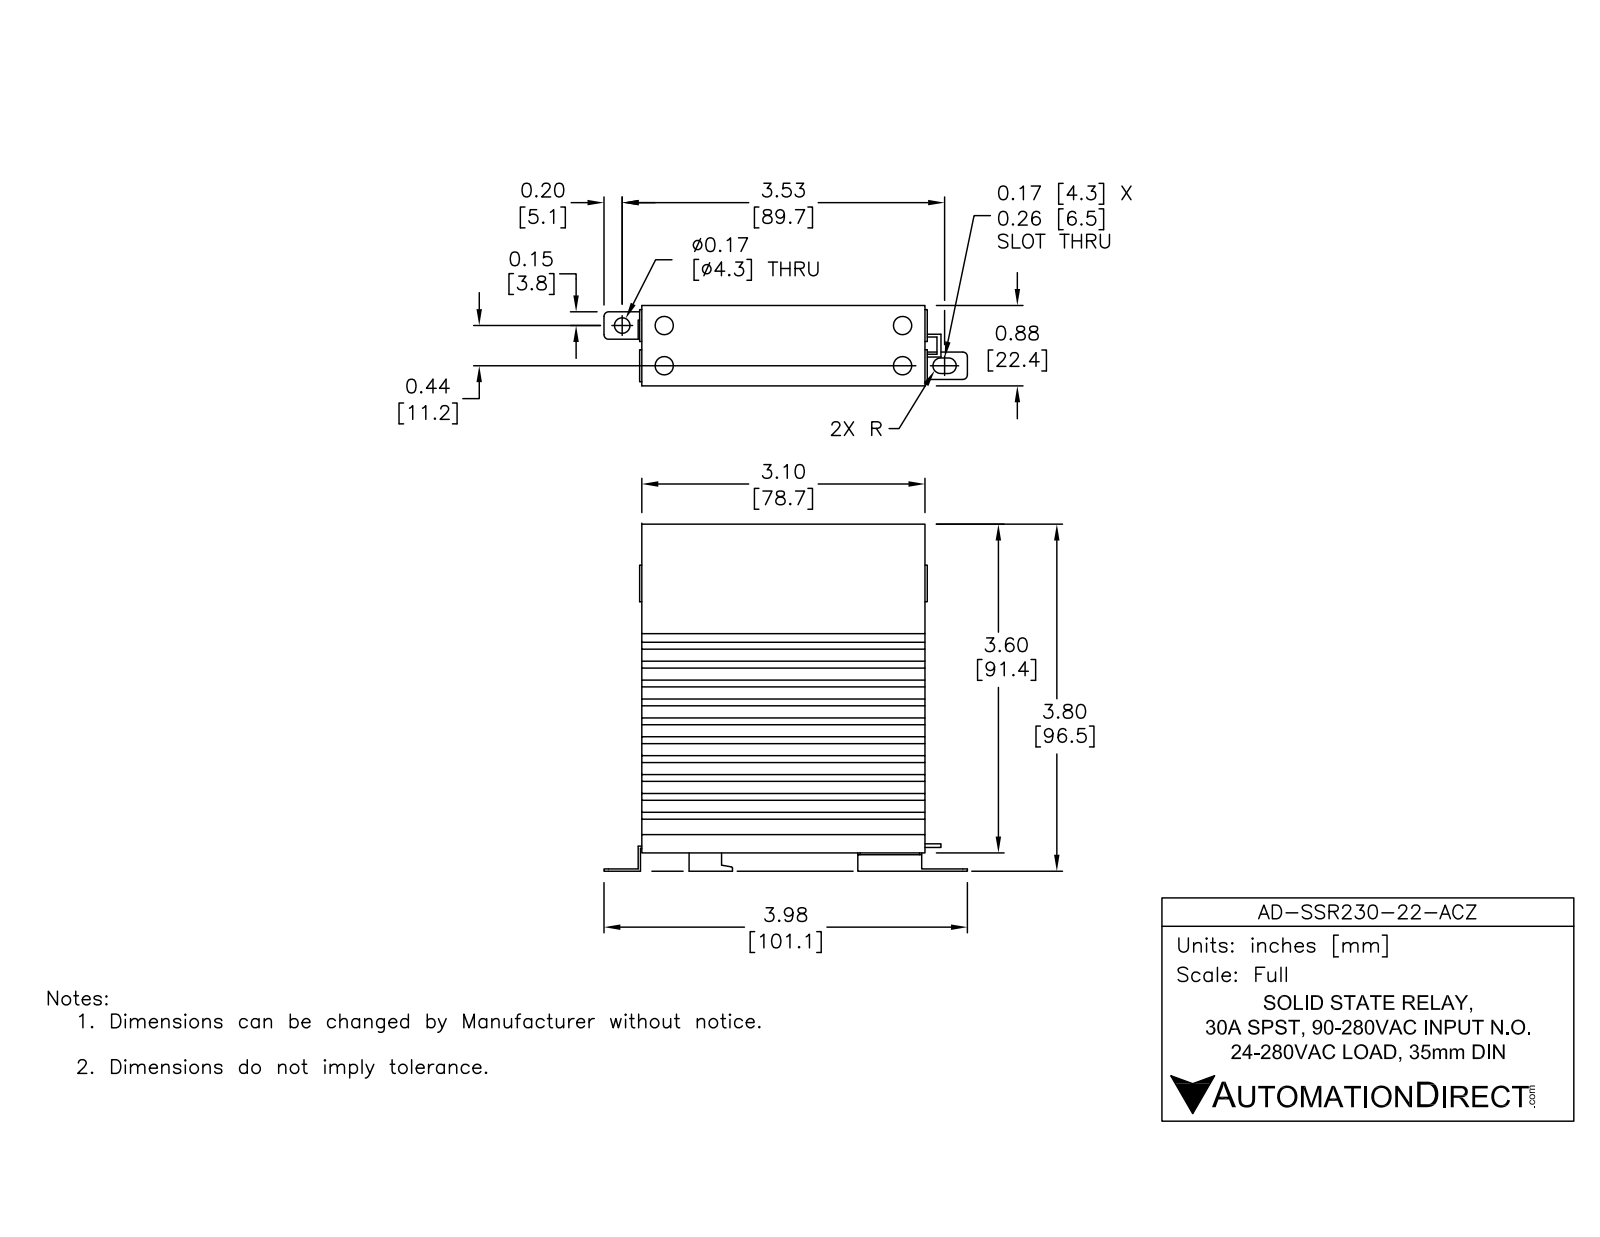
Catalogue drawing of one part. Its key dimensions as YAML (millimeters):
part_name: "AD-SSR230-22-ACZ"
step_written_by: "SolidWorks 2014 (AUTOMOTIVE_DESIGN)"
units: millimeters
bodies: {solids: 1, faces: 215, planar: 195, cylindrical: 20, other: 0}
overall_size: [101.1, 96.5, 22.4]
volume: 116900
surface_area: 48330
round_holes:
  - {diameter: 5.1, count: 4}
  - {diameter: 4.3, count: 1}
partial_cylinders:
  - {radius: 1.3, count: 6}
  - {radius: 2.2, count: 2}
  - {radius: 0.4, count: 1}
face_to_face_distances: [15.7, 5.3, 21, 10.5, 3.4, 12.4, 8.6, 10.5, 1.9, 5.3]
hole_center_spacings: [11.2, 66.3, 67.2, 11.7, 16.2, 78, 78.8]
